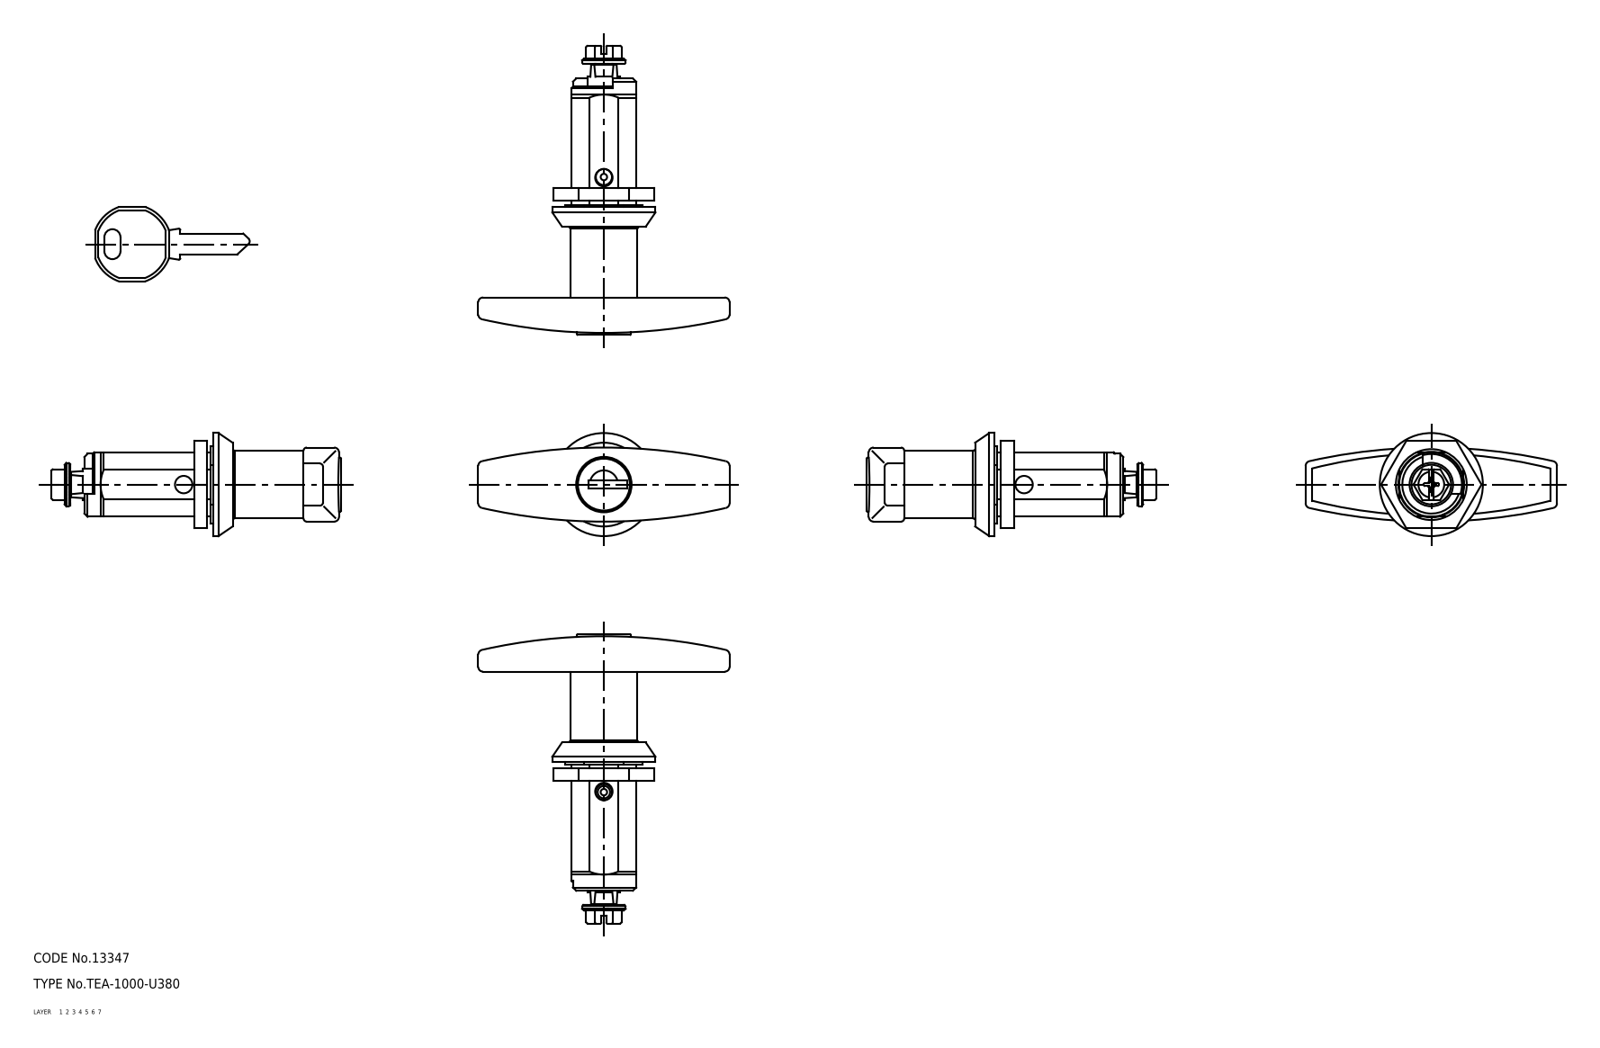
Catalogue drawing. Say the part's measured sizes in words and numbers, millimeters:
The part is named "nut; lock; key; housing (+2 more)". Its 3-D file was written by "CADfix (AUTOMOTIVE_DESIGN)". It is 5 solids with 310 faces: 0 planar, 0 cylindrical and 310 other. Overall it measures 154.11 by 78 by 32 millimeters. Its volume is 37 091 cubic millimeters and its surface area 21 155 square millimeters.
